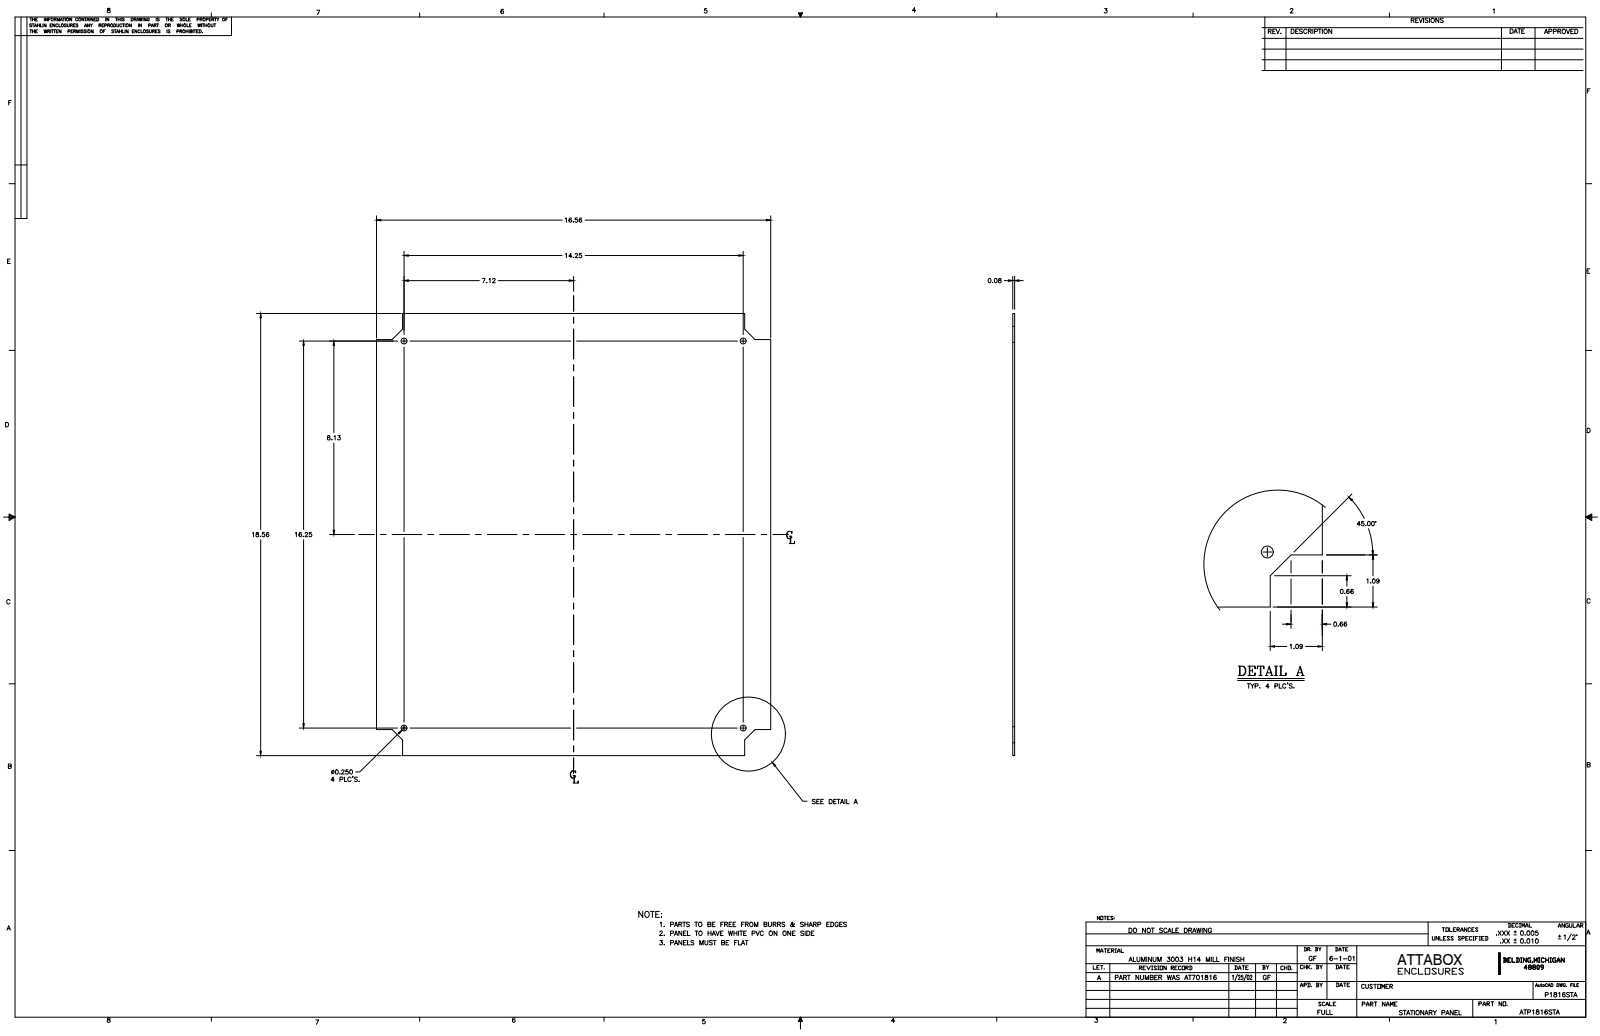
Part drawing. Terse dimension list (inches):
name: P1816STAL
written by: Autodesk Inventor 11 (AUTOMOTIVE_DESIGN)
unit: in
bodies: 1 solid, 22 faces (18 planar, 4 cylindrical, 0 other)
size: 18.563 × 16.563 × 0.08
volume: 24.23 in³; area: 611.5 in²
holes: 4× ⌀0.25
face distances: 0.08, 16.562, 18.562, 1.094, 15.468, 17.468, 14.374, 16.374, 22.357
hole spacings: 14.25, 16.25, 21.613
